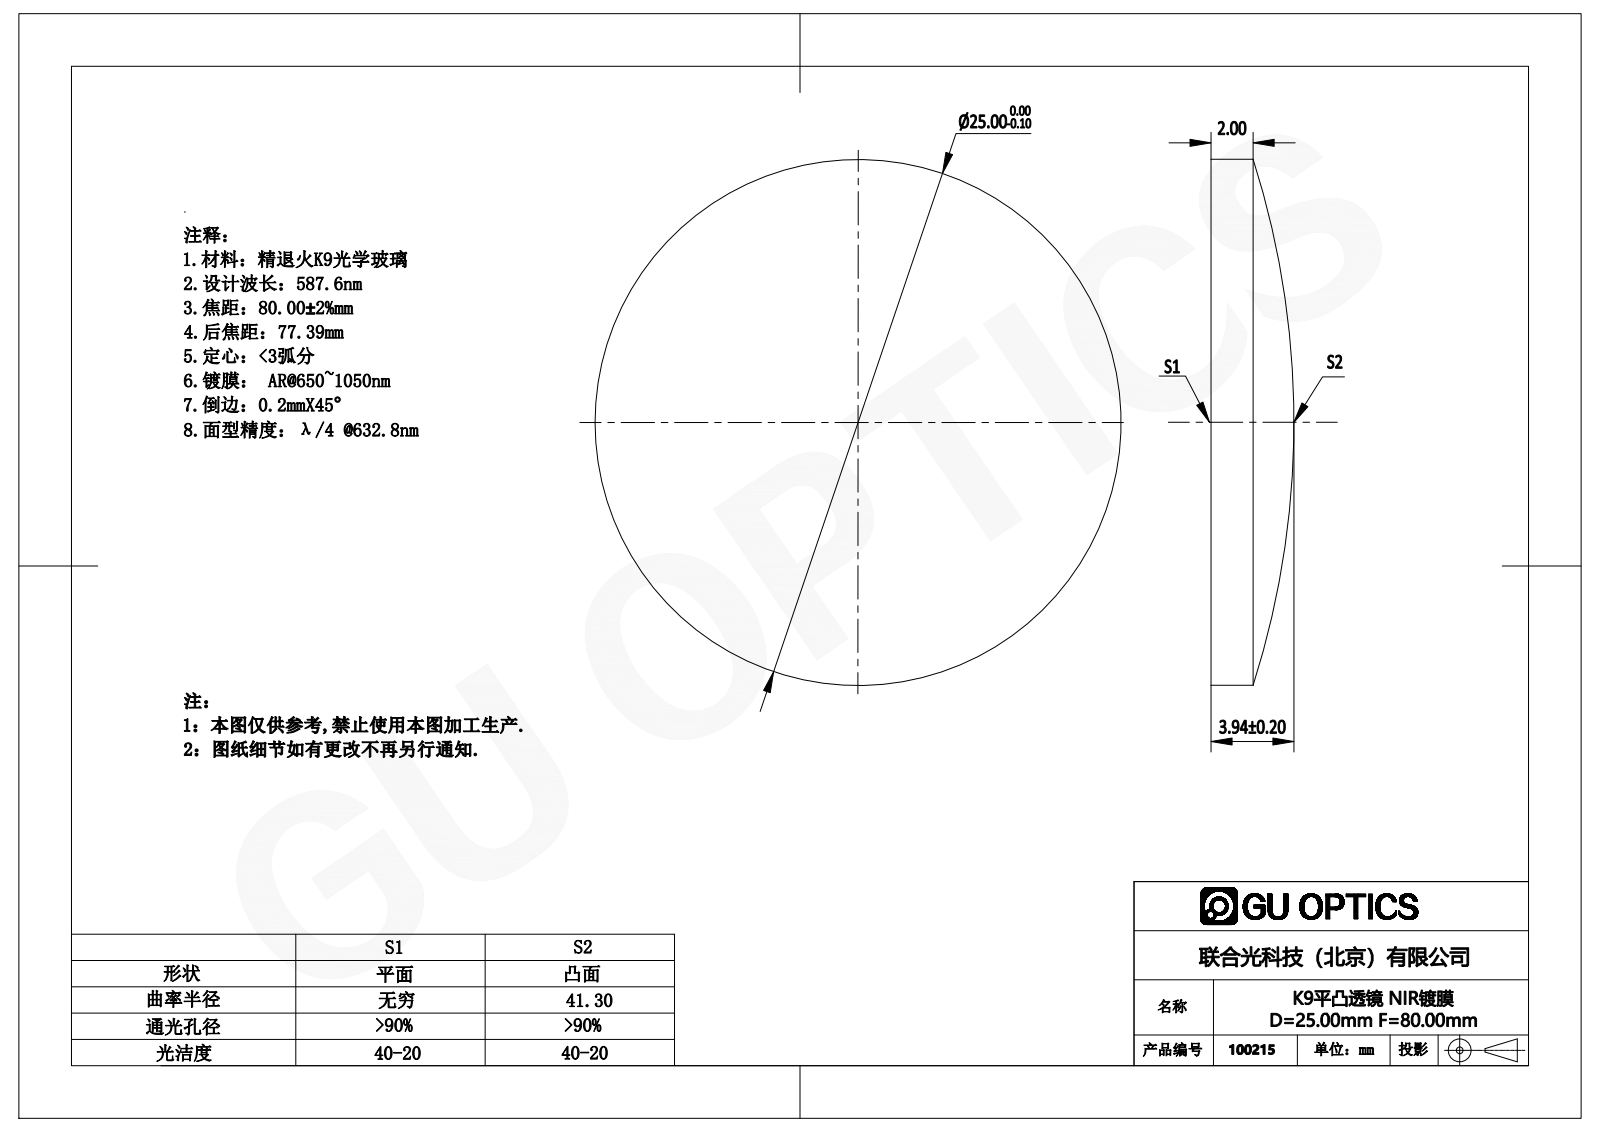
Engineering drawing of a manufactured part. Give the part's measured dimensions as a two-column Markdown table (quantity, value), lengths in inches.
| quantity | value |
| --- | --- |
| part name | 100215 |
| STEP written by | SolidWorks 2016 (AUTOMOTIVE_DESIGN) |
| units | inches |
| bodies | 1 solid, 5 faces (1 planar, 2 cylindrical, 2 other) |
| overall size | 0.984 × 0.984 × 0.155 |
| volume | 0.089 in³ |
| surface area | 1.784 in² |
| round bosses / shafts (diameter × count) | 0.984 × 1 |
